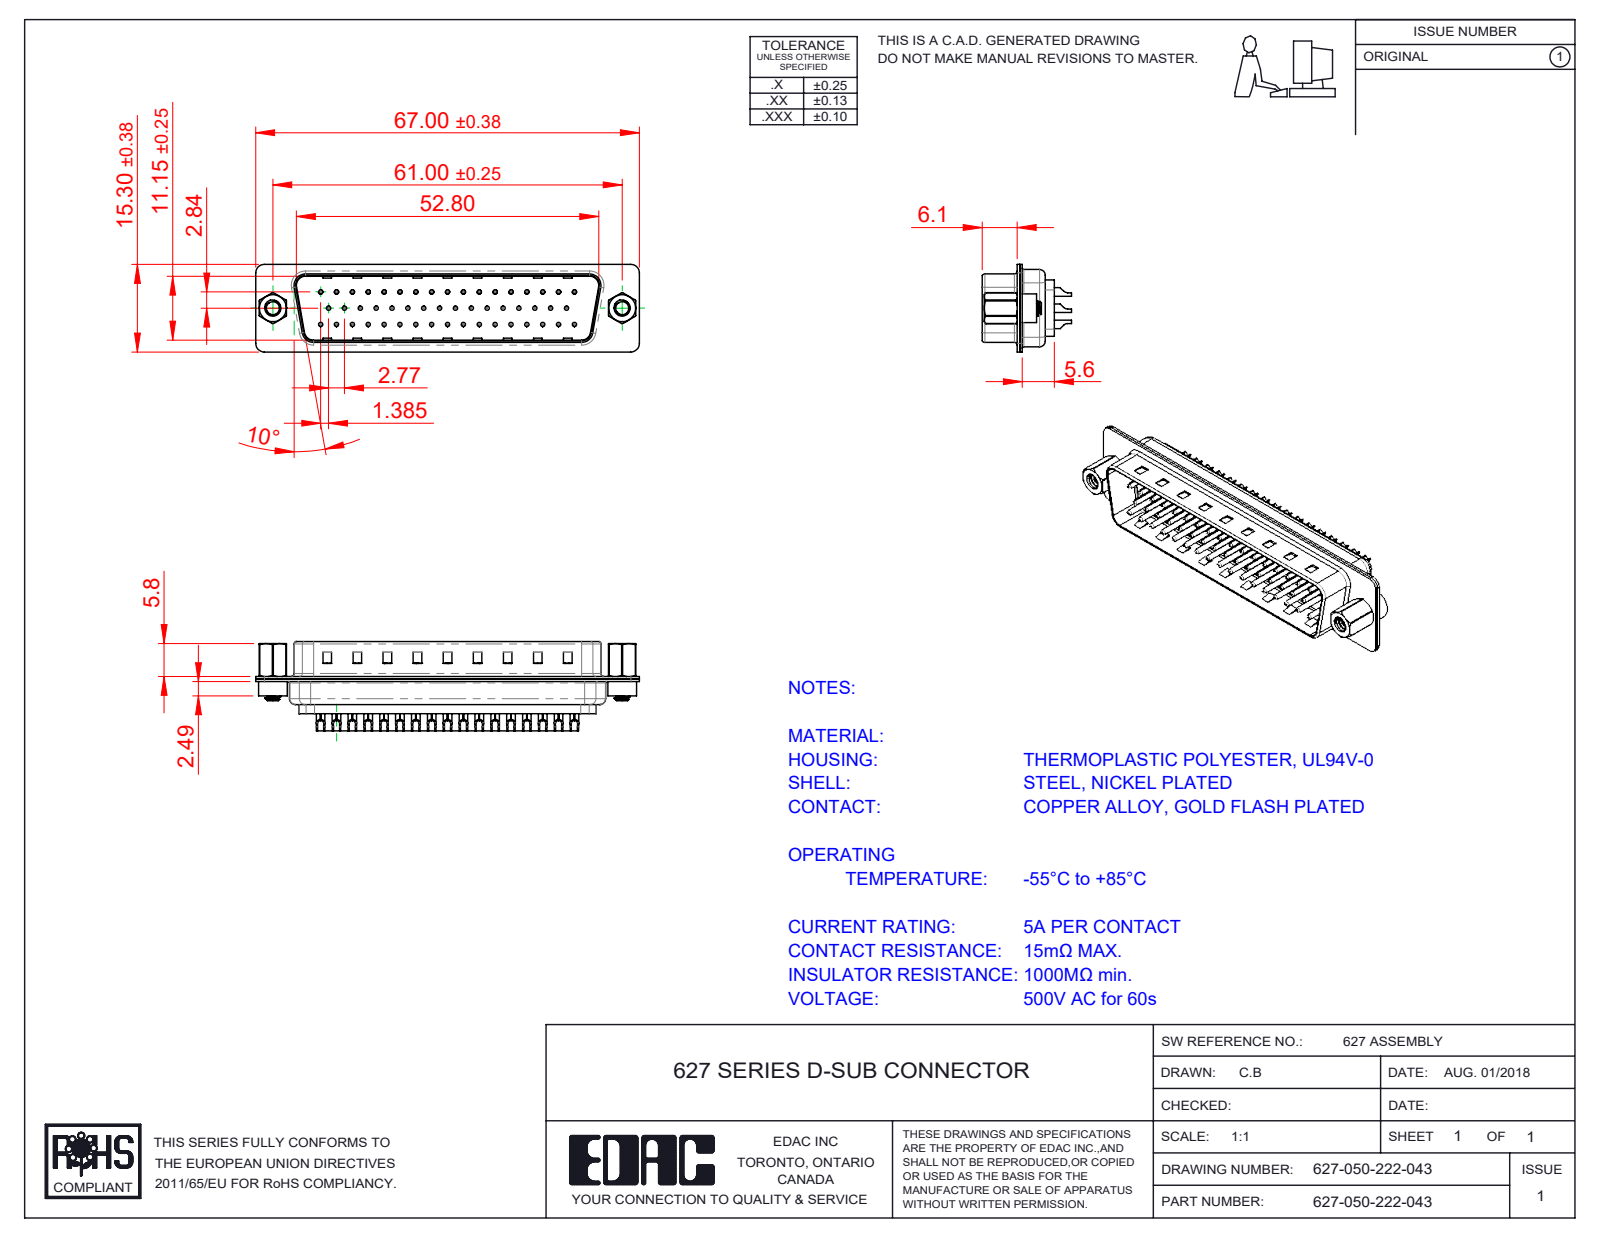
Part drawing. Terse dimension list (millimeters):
name: 627 Contact Row 1_22L; 627 Contact Row 2_22M; 627 Shell Rear_50 Contacts; 627 4-40 Hex Standoff (+5 more)
written by: SolidWorks 2020 (CONFIG_CONTROL_DESIGN)
unit: mm
bodies: 57 solids, 3734 faces (925 planar, 1661 cylindrical, 1148 other)
size: 67 × 15.6 × 15.3
volume: 4 659 mm³; area: 13 246 mm²
holes: 58× ⌀1.6, 50× ⌀0.35, 50× ⌀1.1, 8× ⌀0.75, 8× ⌀2, 2× ⌀2.26, 2× ⌀2.29, 2× ⌀4, 2× ⌀4.8
bosses: 50× ⌀2, 50× ⌀1.5, 50× ⌀0.75, 2× ⌀5, 2× ⌀4.9, 2× ⌀2.79
rounds: 16× R1.5, 12× R2, 8× R0.5, 8× R1.6, 7× R1, 4× R0.25, 4× R0.6, 4× R0.65
face distances: 0.4, 0.45, 11.55, 0.9, 6.05, 6.5, 0.78, 1.95, 0.77, 12.33
hole spacings: 2.77, 3.16, 5.54, 8.31, 11.08, 13.85, 16.62, 19.39
